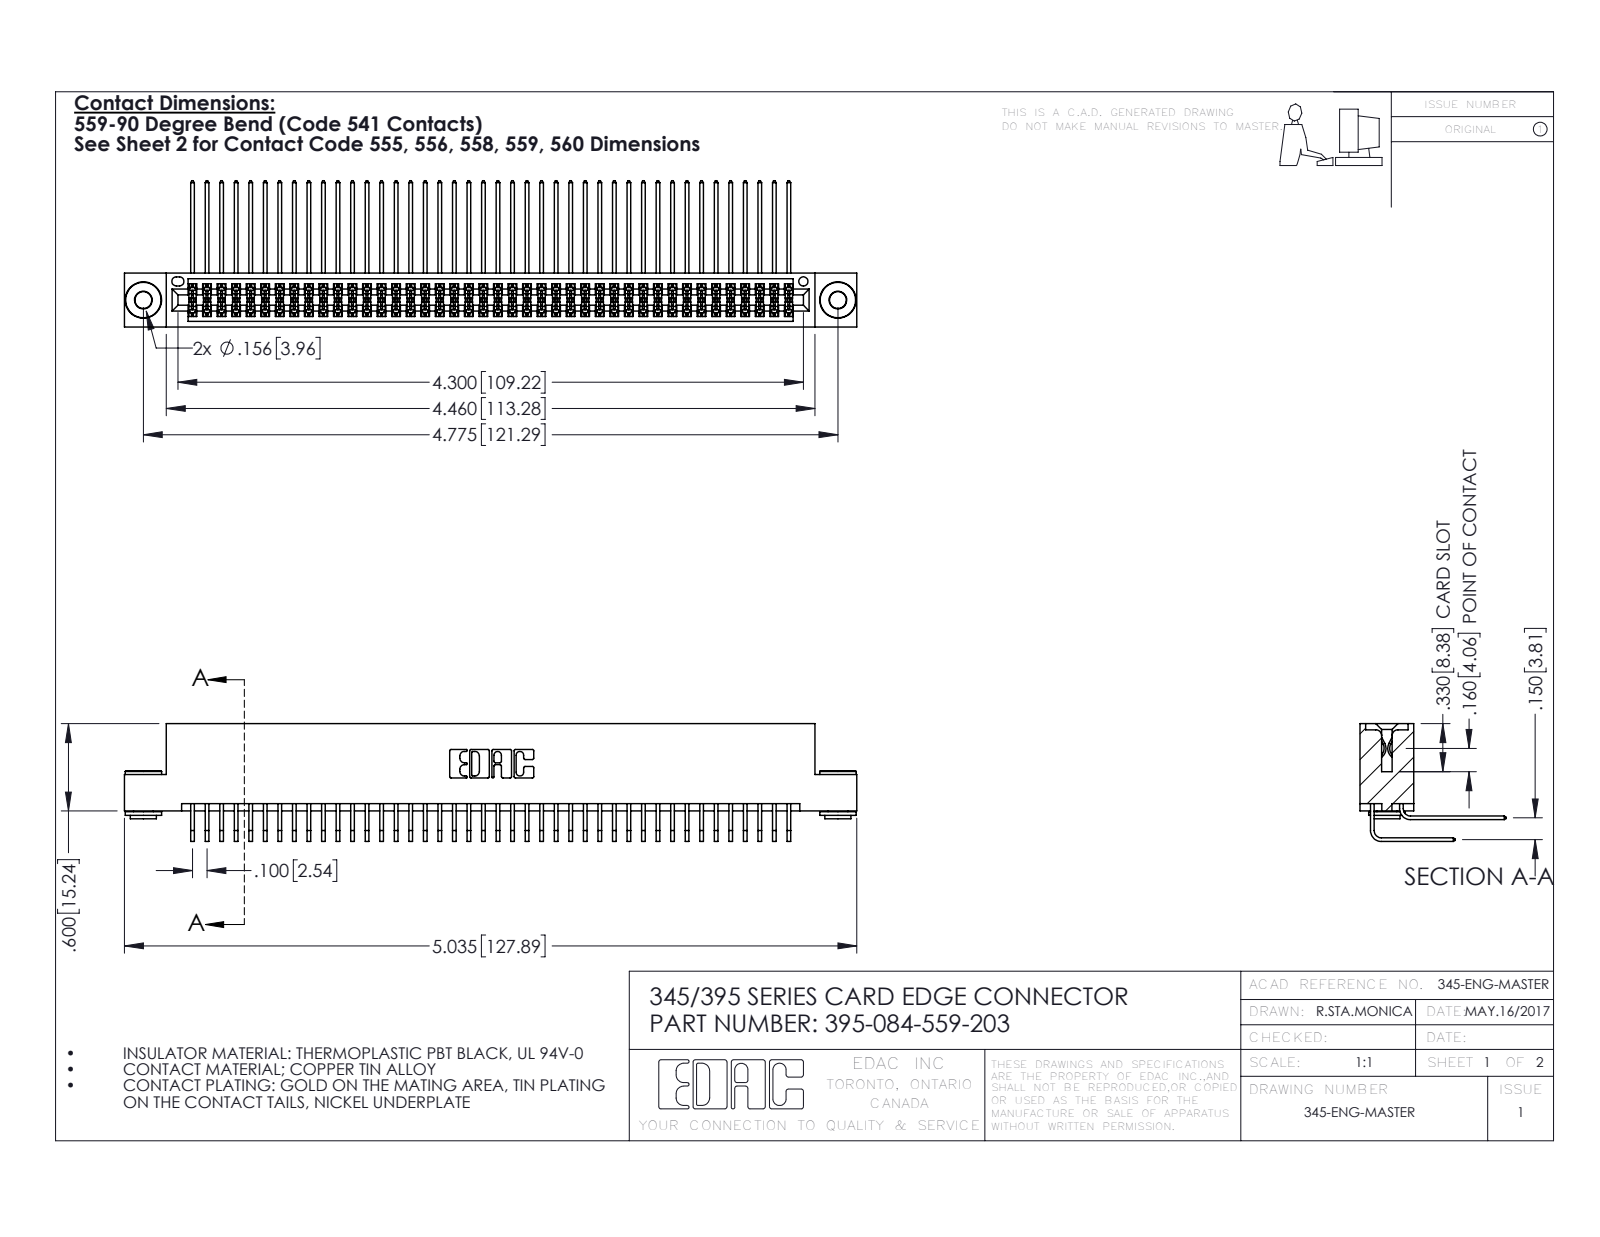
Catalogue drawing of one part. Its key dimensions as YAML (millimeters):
part_name: "395-084-559-203; 345 Part_Flush Mounting Lugs - 0.156 Dia-TH; 345-292-001_558 559 Tail - 1; 345-250-002_345-250-002-102 (+1 more)"
step_written_by: "SolidWorks 2016 (CONFIG_CONTROL_DESIGN)"
units: millimeters
bodies: {solids: 87, faces: 4532, planar: 3030, cylindrical: 1494, other: 8}
overall_size: [127.9, 25.5, 20.5]
volume: 12900
surface_area: 21590
round_holes:
  - {diameter: 2.9, count: 2}
  - {diameter: 4, count: 2}
  - {diameter: 1.6, count: 1}
round_bosses_or_shafts:
  - {diameter: 6.4, count: 2}
  - {diameter: 4.6, count: 2}
  - {diameter: 3.5, count: 2}
partial_cylinders:
  - {radius: 0.2, count: 126}
  - {radius: 0.3, count: 22}
  - {radius: 0.2, count: 6}
  - {radius: 0.8, count: 6}
  - {radius: 0.7, count: 3}
  - {radius: 0.4, count: 2}
  - {radius: 0.5, count: 2}
  - {radius: 0.6, count: 2}
face_to_face_distances: [1.8, 7.6, 5.1, 9.4, 0.6, 2.5, 6.9, 5.7, 4.4, 3.8]
hole_center_spacings: [6.9, 115.3, 121.3]
